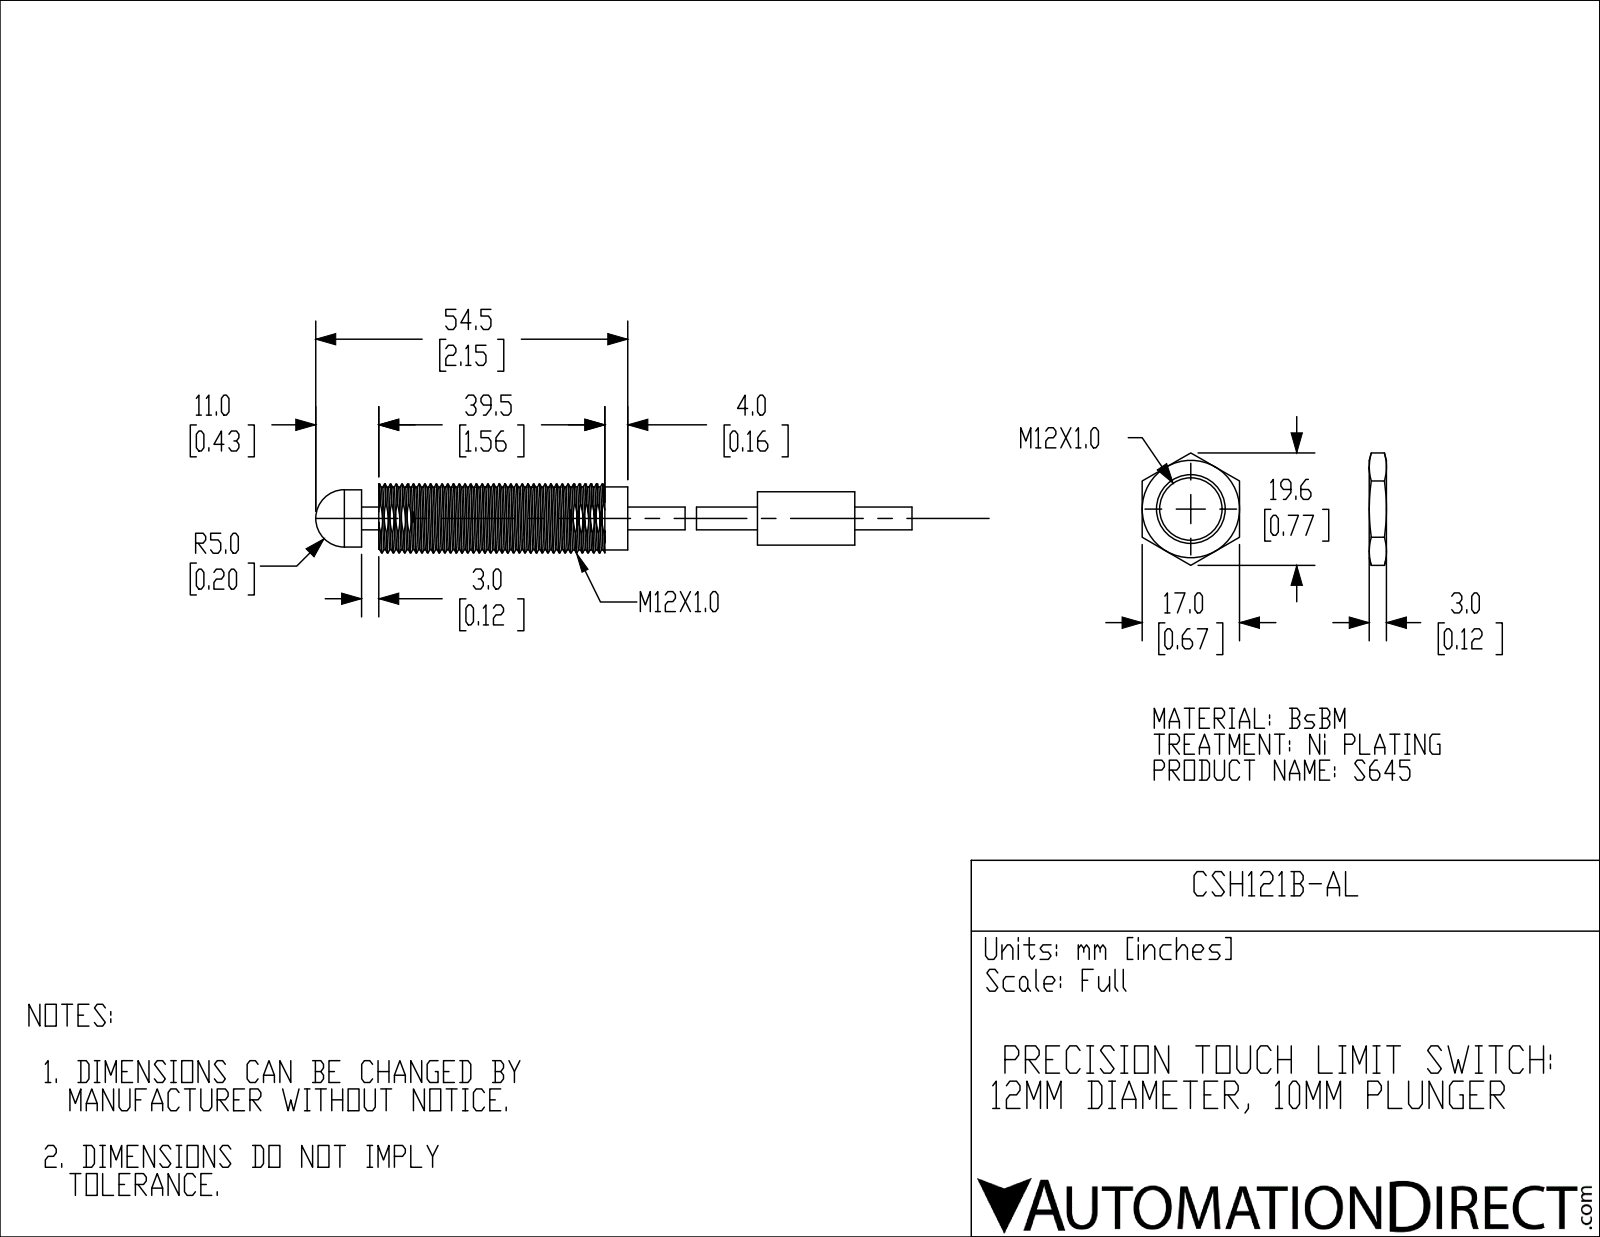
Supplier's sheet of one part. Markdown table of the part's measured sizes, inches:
| quantity | value |
| --- | --- |
| part name | CSH121A-AL |
| STEP written by | SolidWorks 2018 (AUTOMOTIVE_DESIGN) |
| units | inches |
| bodies | 2 solids, 28 faces (16 planar, 8 cylindrical, 4 other) |
| overall size | 4.1 × 0.472 × 0.472 |
| volume | 0.42 in³ |
| surface area | 4.946 in² |
| round bosses / shafts (diameter × count) | 0.472 × 1, 0.433 × 1, 0.394 × 1, 0.366 × 1, 0.157 × 1 |
| main face-to-face distances | 1.713, 1.561, 0.118, 1.831, 0.433, 2.722, 3.391, 2.604, 3.273, 0.891 |
